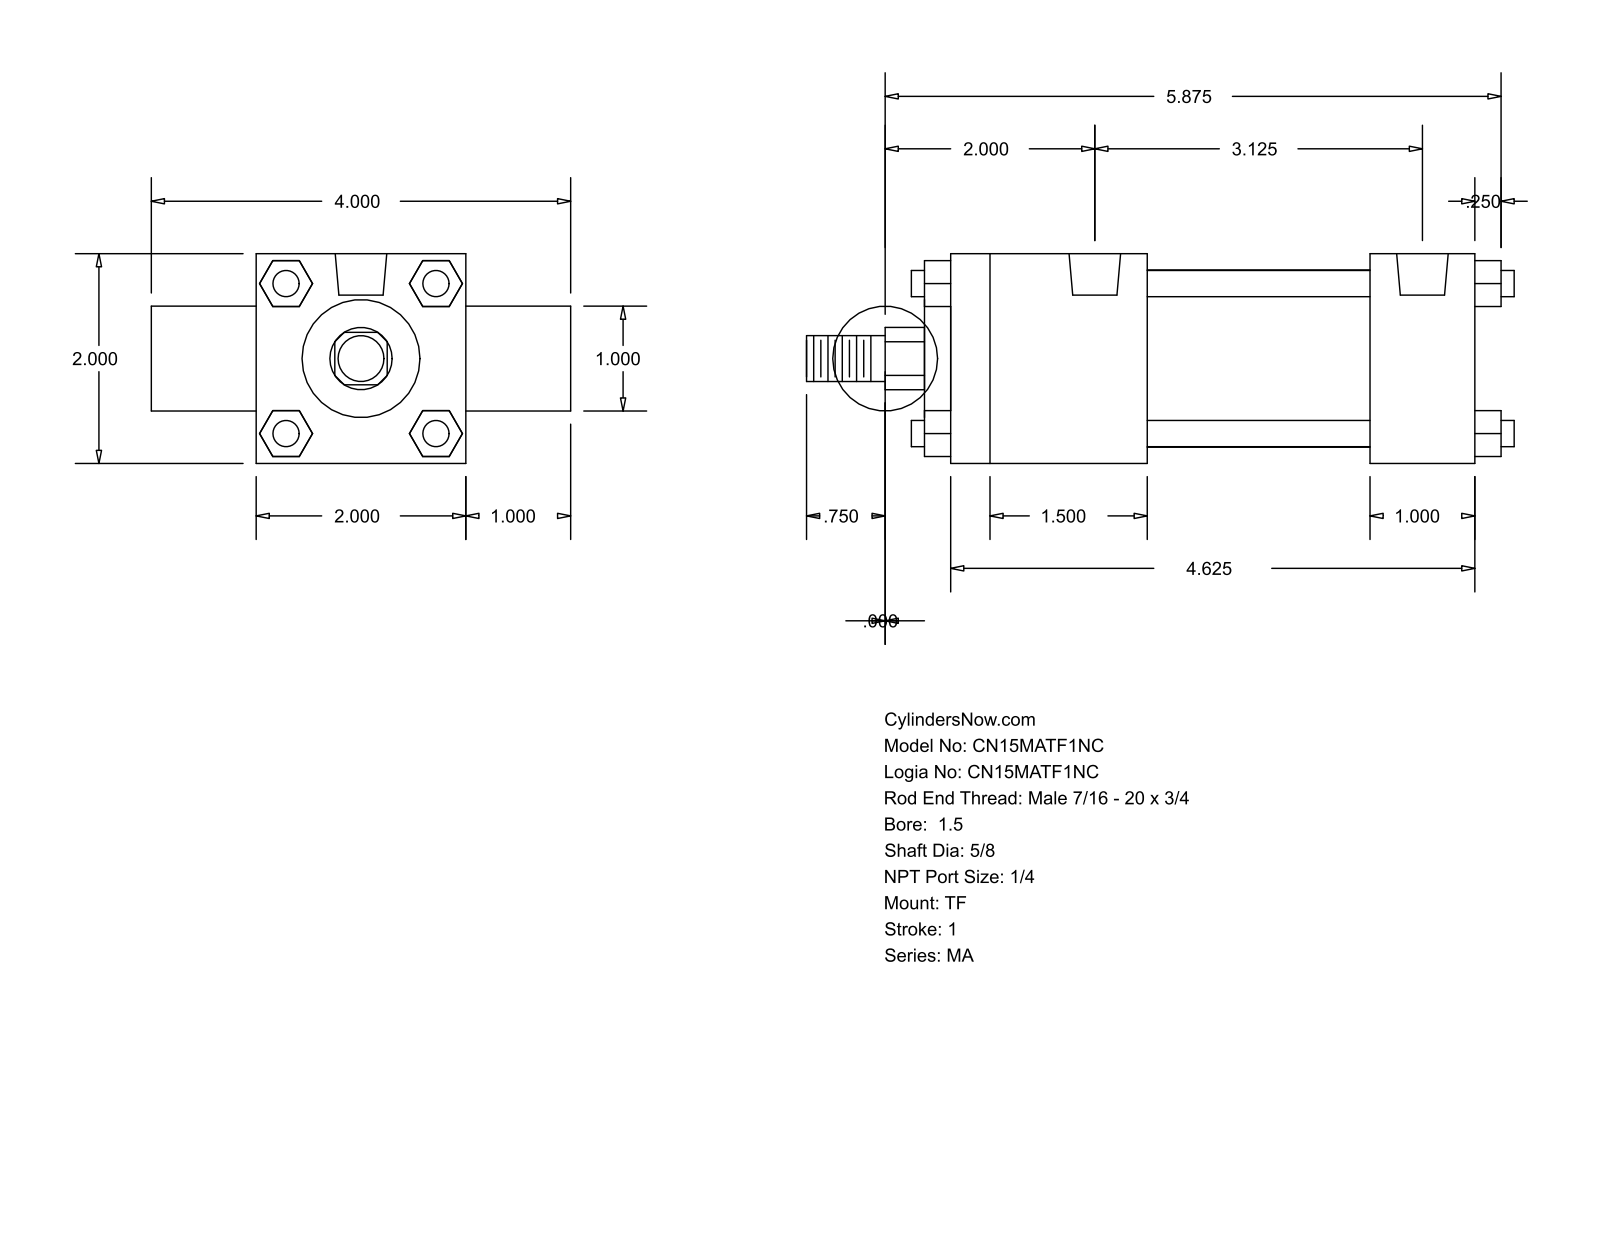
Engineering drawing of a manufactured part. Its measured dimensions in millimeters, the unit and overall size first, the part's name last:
Units: millimetres
Overall size (bounding box): 171.45 × 101.6 × 50.8
Round holes (diameter × count): ⌀7.94 ×3, ⌀12.49 ×2
Round bosses / shafts (diameter × count): ⌀6.35 ×4, ⌀42.93 ×1, ⌀28.57 ×1, ⌀25.4 ×1, ⌀15.88 ×1, ⌀11.11 ×1
Partial cylindrical surfaces — rounded edges, fillets, slot ends (radius × count): R7.54 ×1
Main face-to-face distances: 50.8, 53.97, 127, 25.4, 76.2, 47.62, 101.59, 79.38, 25.41, 6.35
Hole centre spacings: 79.38
Bodies: 0 solids, 120 faces (92 planar, 28 cylindrical, 0 other)
Part name (STEP PRODUCT): MA_TF__0150_0.625
STEP written by: GSSL Pune (CONFIG_CONTROL_DESIGN)
